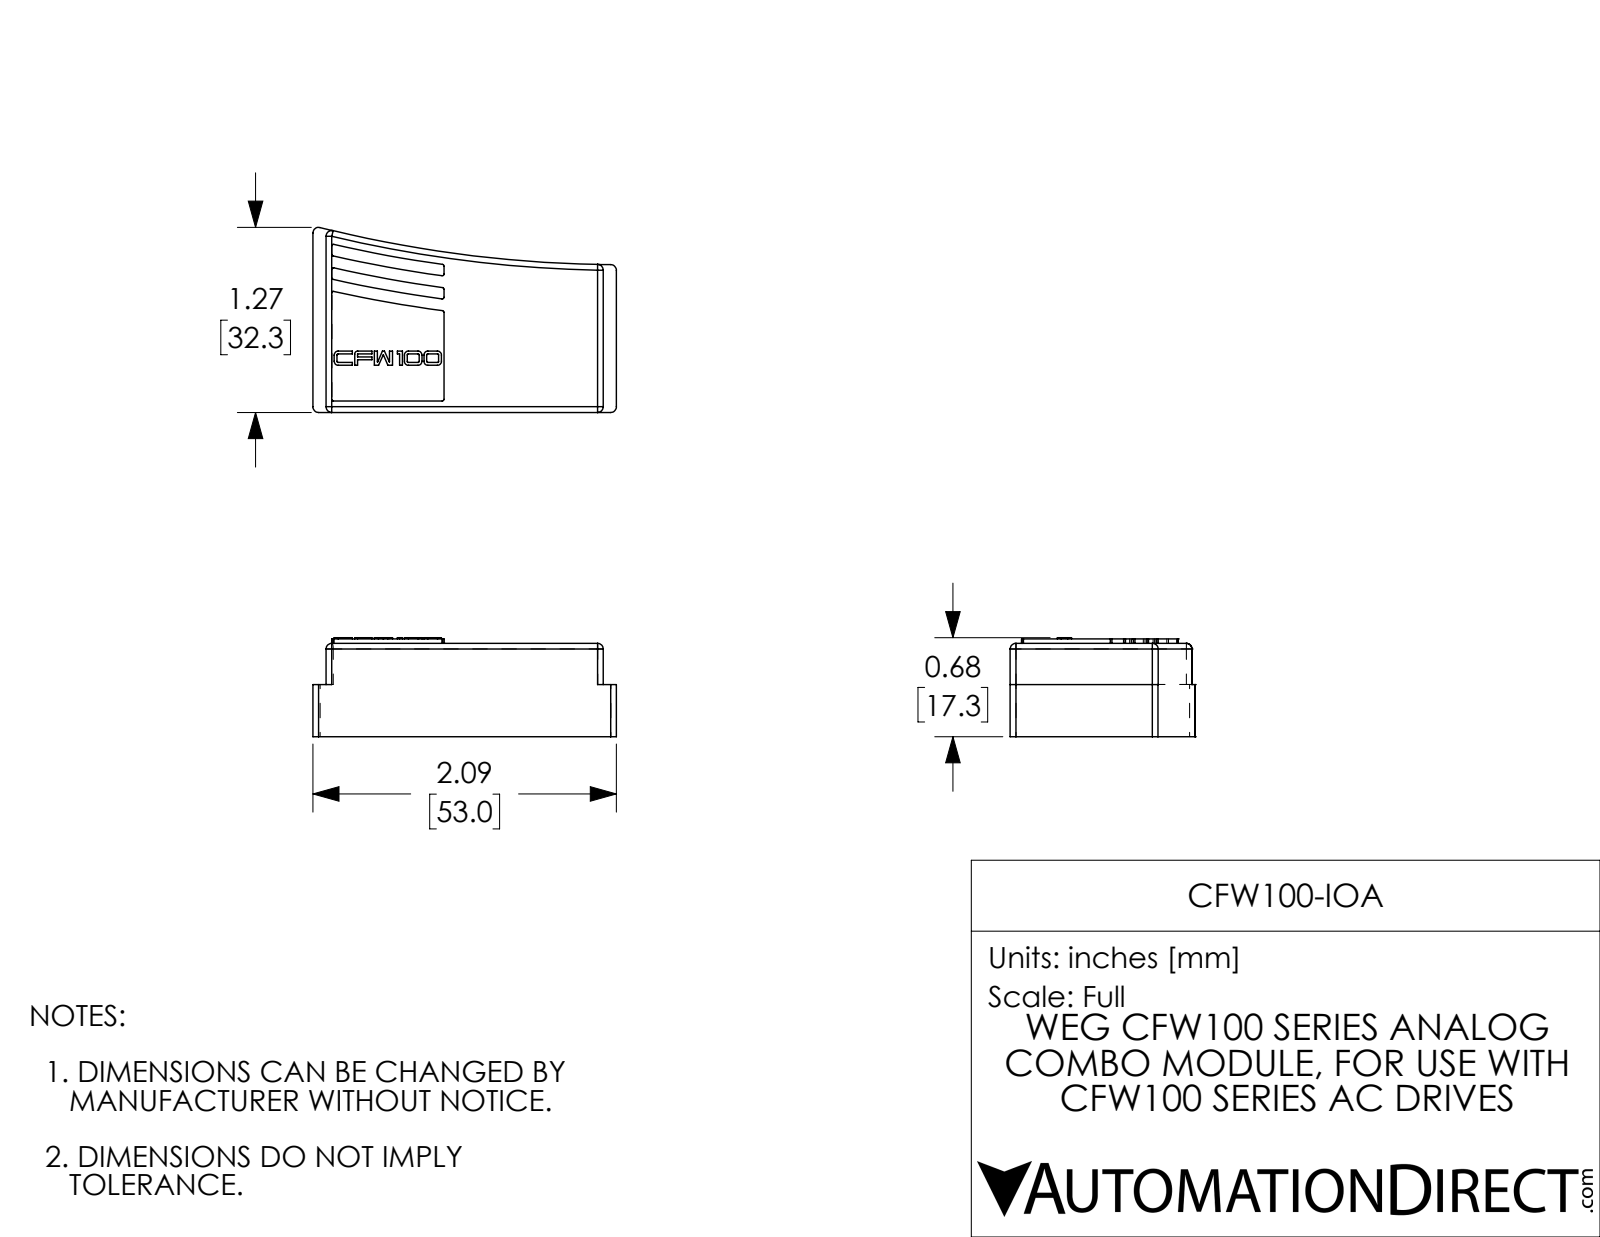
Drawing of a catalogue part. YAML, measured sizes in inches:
part_name: "IGS CFW100-IOAR"
step_written_by: "SolidWorks 2017 (AUTOMOTIVE_DESIGN)"
units: inches
bodies: {solids: 1, faces: 145, planar: 83, cylindrical: 48, other: 14}
overall_size: [2.087, 1.272, 0.68]
volume: 1.439
surface_area: 8.737
partial_cylinders:
  - {radius: 0.039, count: 11}
  - {radius: 0.008, count: 10}
  - {radius: 0.028, count: 10}
  - {radius: 0.012, count: 1}
  - {radius: 0.012, count: 1}
  - {radius: 0.012, count: 1}
  - {radius: 0.021, count: 1}
  - {radius: 8.52, count: 1}
face_to_face_distances: [0.642, 0.672, 0.03, 0.091, 1.996, 2.087, 1.906, 0.358, 0.283, 0.313]
